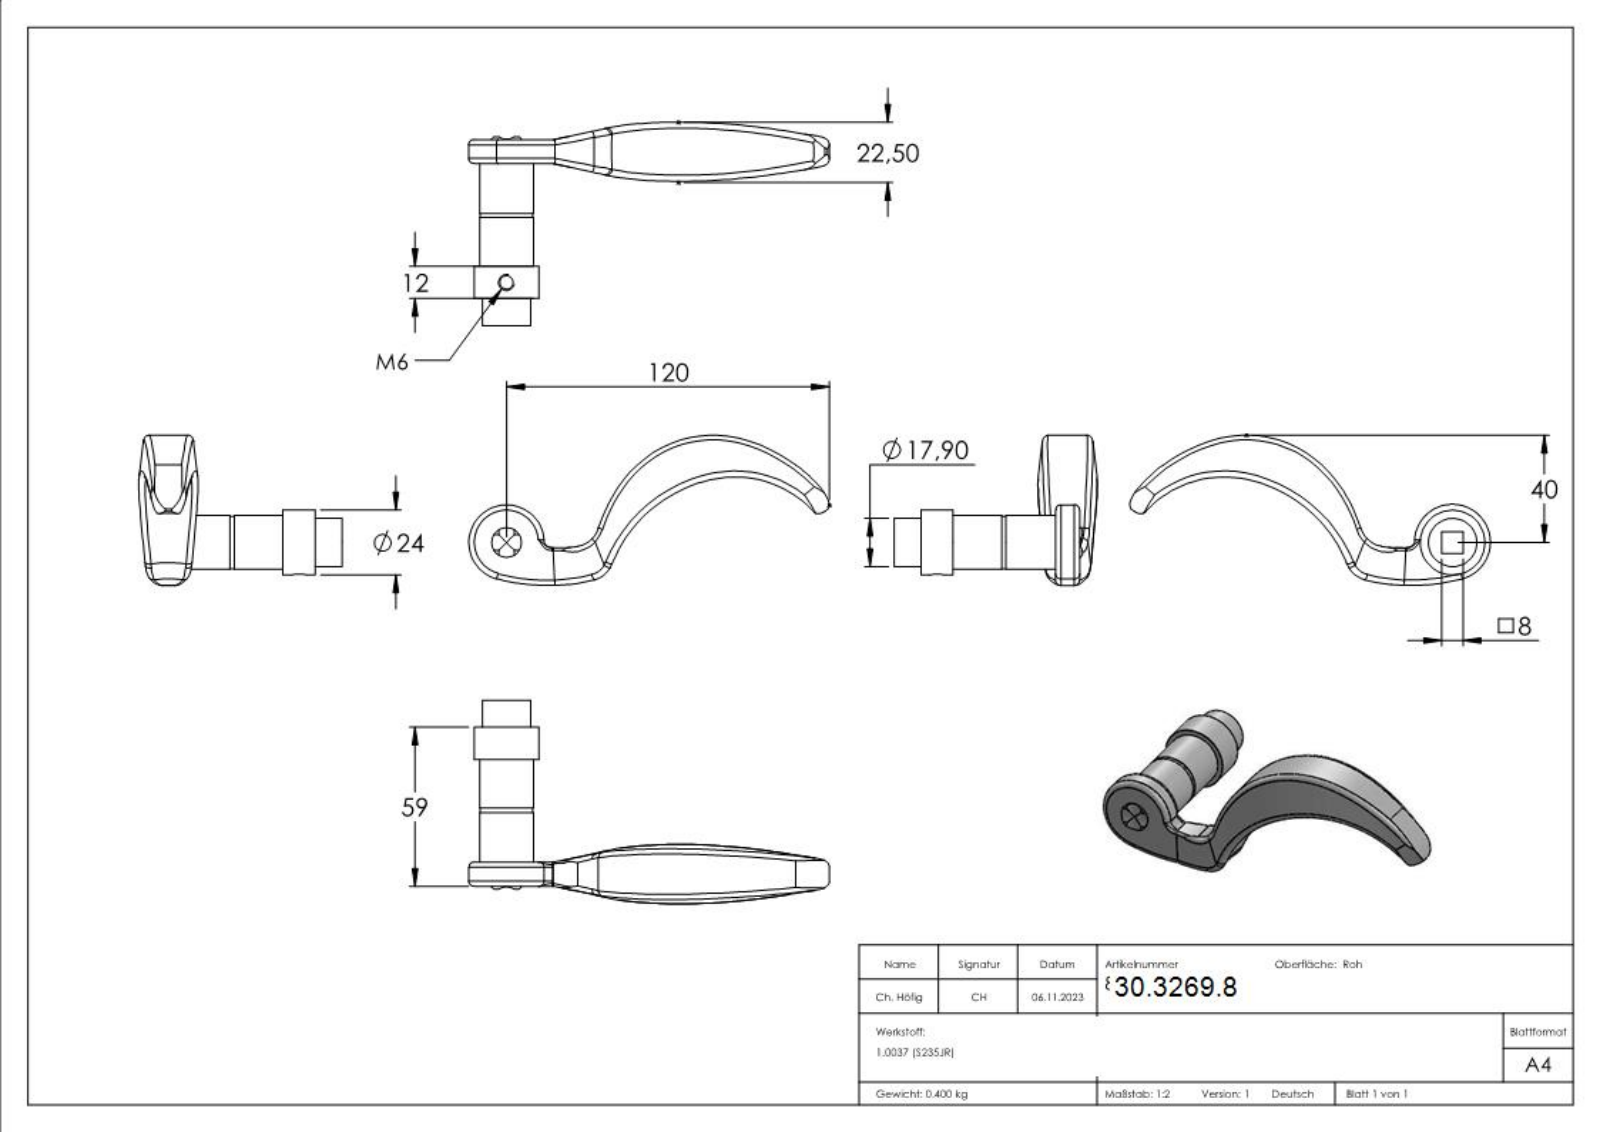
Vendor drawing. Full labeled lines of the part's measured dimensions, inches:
Part name (STEP PRODUCT): 8012
STEP written by: SolidWorks 2018 (CONFIG_CONTROL_DESIGN)
Units: inches
Bodies: 1 solid, 237 faces (101 planar, 15 cylindrical, 121 other)
Overall size (bounding box): 5.273 × 2.973 × 2.2
Volume: 3.126 in³ · Surface area: 22.98 in²
Round holes (diameter × count): ⌀0.197 ×1
Round bosses / shafts (diameter × count): ⌀0.945 ×1, ⌀0.787 ×1, ⌀0.764 ×1, ⌀0.705 ×1, ⌀0.433 ×1
Partial cylindrical surfaces — rounded edges, fillets, slot ends (radius × count): R0.217 ×2, R0.118 ×1, R0.551 ×1, R2.189 ×1, R2.741 ×1
Main face-to-face distances: 0.315, 0.354, 1.969, 2.323, 0.394, 2.362, 2.717, 0.866, 0.472, 1.496
